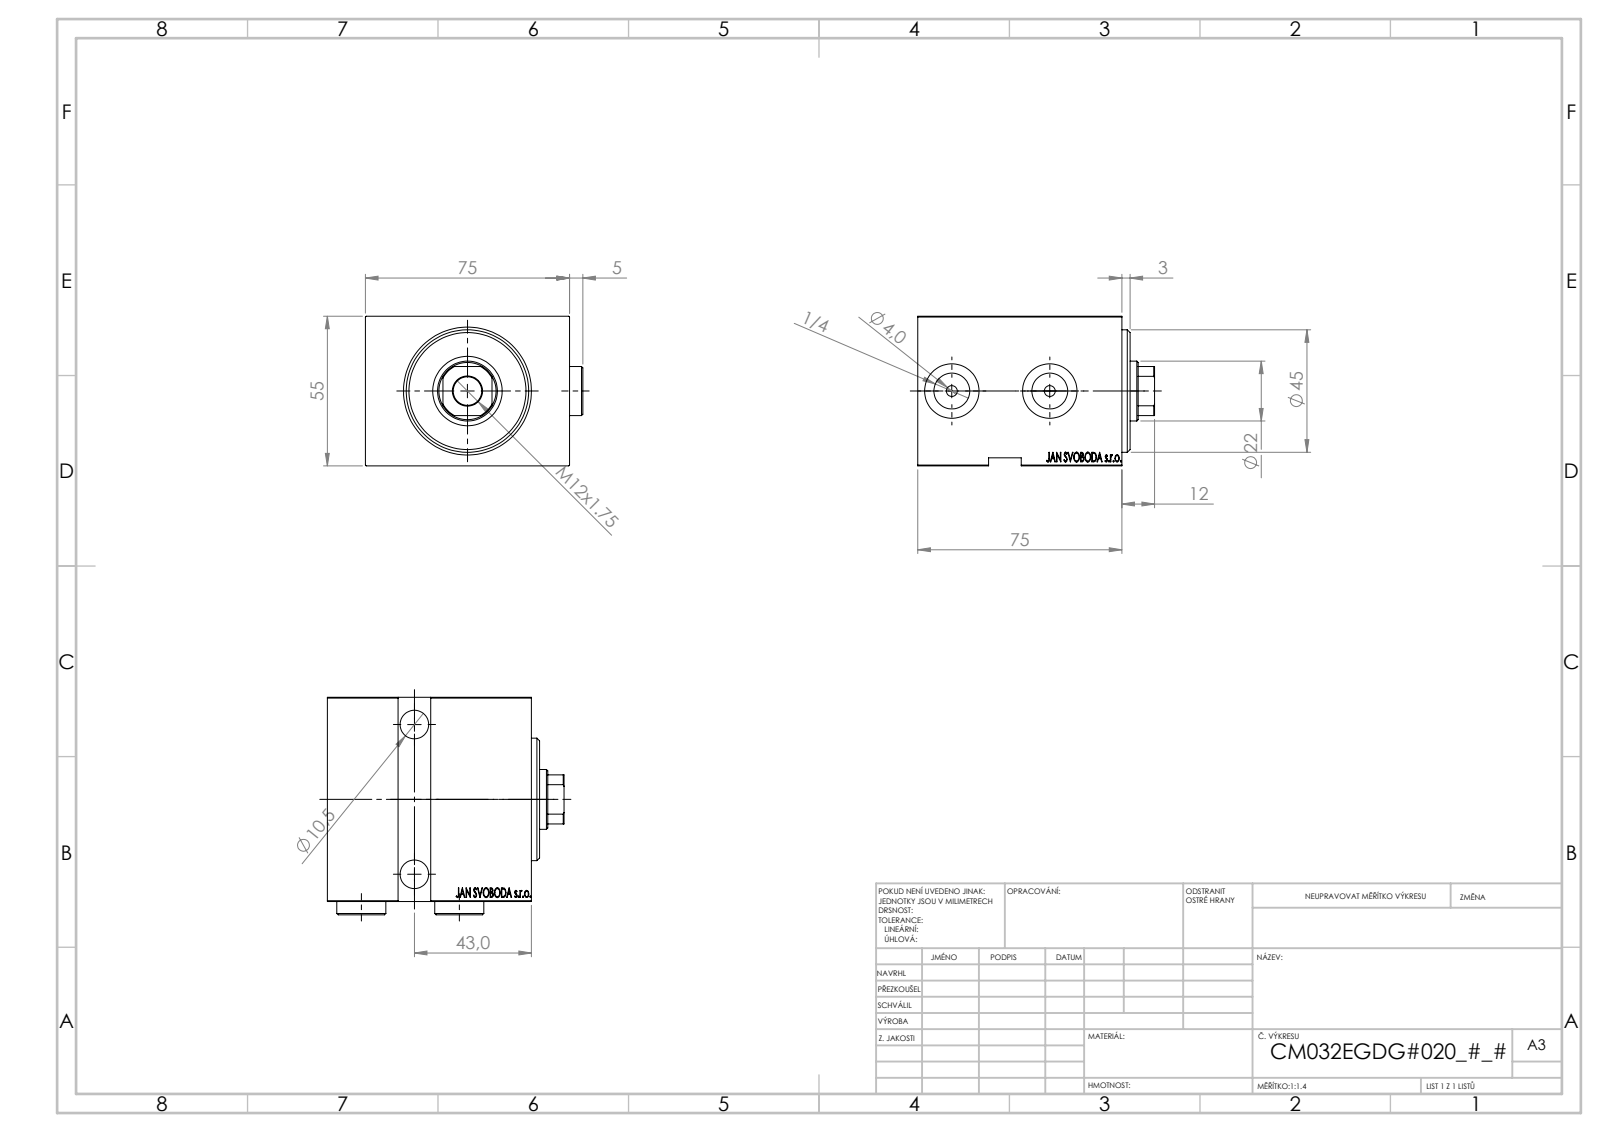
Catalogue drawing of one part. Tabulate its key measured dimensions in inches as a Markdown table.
| quantity | value |
| --- | --- |
| part name | V450CM_E_Body; V450CM_E_VCP; Zatka_OIL_PORT; V450CM_VC_B |
| STEP written by | SolidWorks 2019 (CONFIG_CONTROL_DESIGN) |
| units | inches |
| bodies | 5 solids, 899 faces (443 planar, 58 cylindrical, 398 other) |
| overall size | 3.425 × 3.146 × 2.165 |
| volume | 17.38 in³ |
| surface area | 86.78 in² |
| round holes (diameter × count) | 0.413 × 3, 0.157 × 2, 0.518 × 2, 0.65 × 2, 0.787 × 2, 0.866 × 1, 1.004 × 1, 1.26 × 1, 1.772 × 1 |
| round bosses / shafts (diameter × count) | 0.709 × 2, 1.339 × 1 |
| partial cylindrical surfaces (radius × count) | 0.413 × 1 |
| main face-to-face distances | 2.953, 2.165, 0.197, 0.118, 2.559, 0.394, 2.756, 2.362, 2.949, 0.472 |
| hole center spacings | 1.417, 2.165 |
